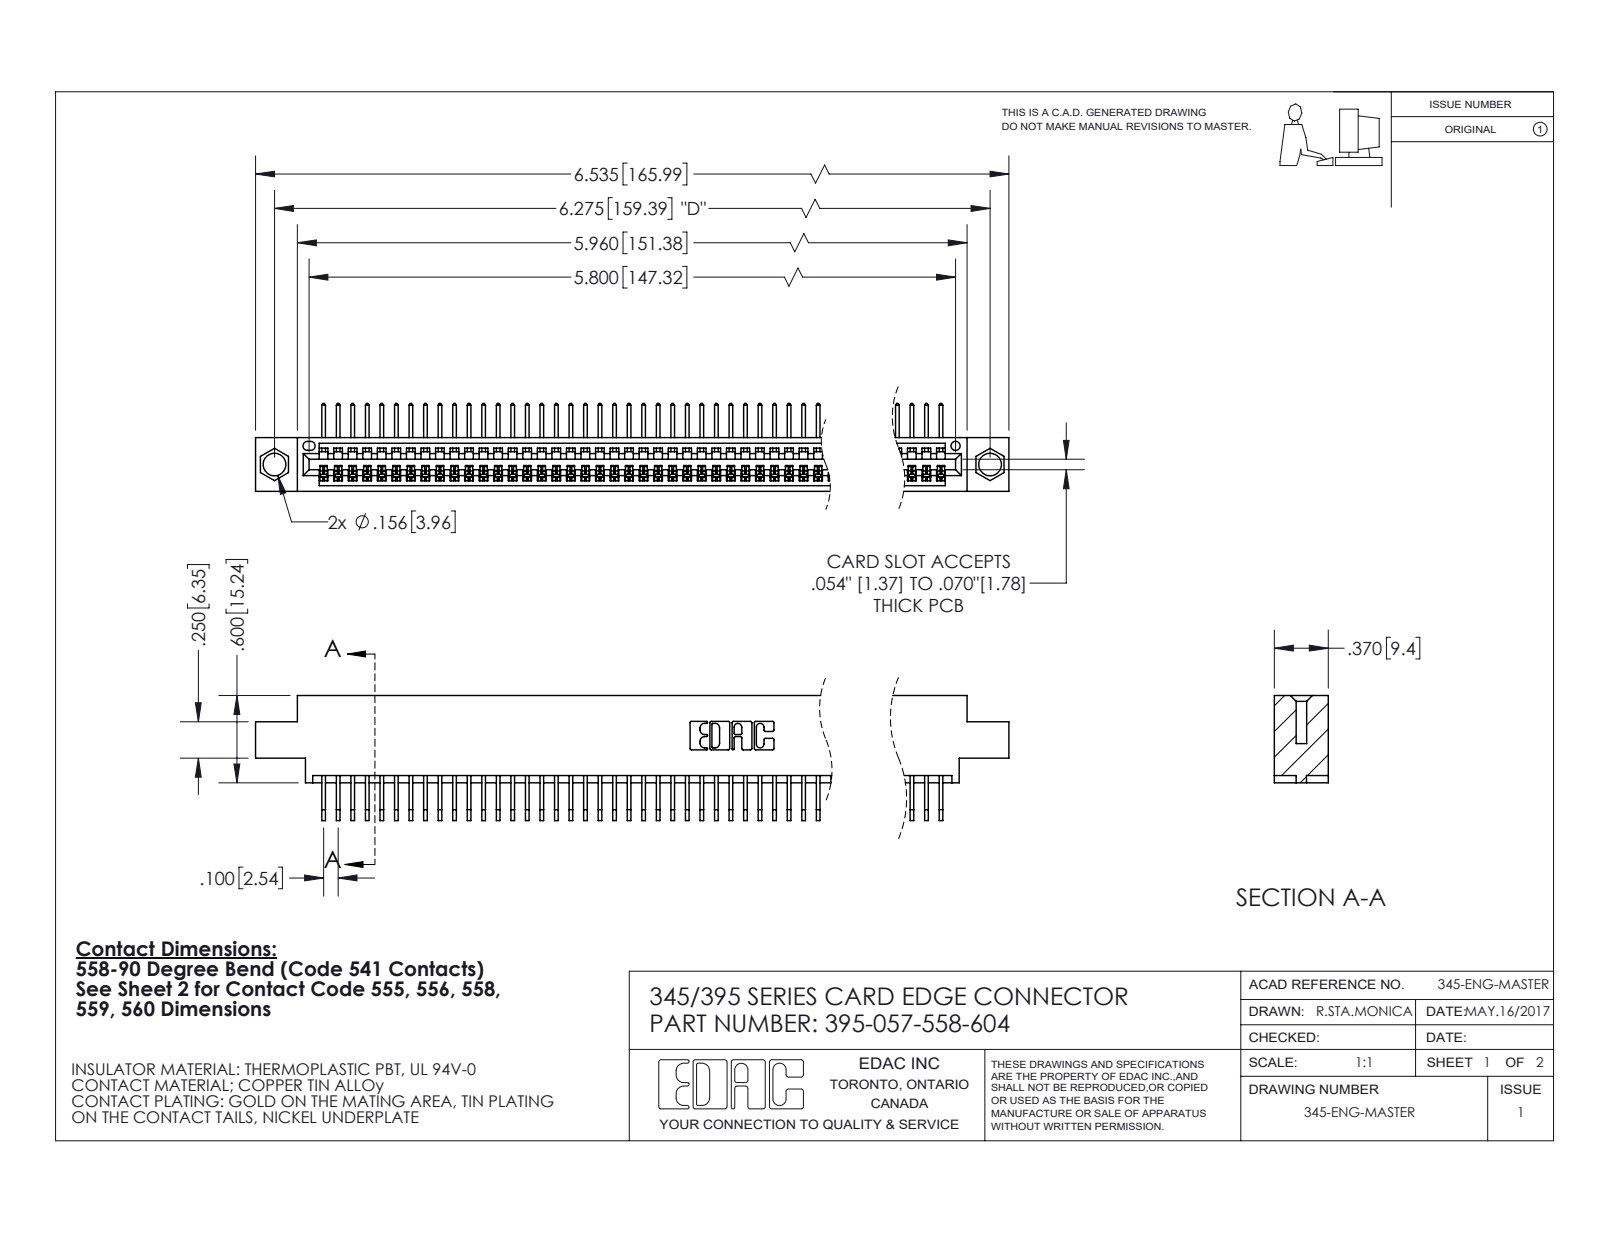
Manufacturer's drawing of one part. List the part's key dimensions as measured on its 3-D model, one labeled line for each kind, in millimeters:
Part name (STEP PRODUCT): 345 Part_0.170 Offset - 0.156 Dia-TI; 345-292-001_558 Tail - 2; 395-057-558-604
STEP written by: SolidWorks 2020 (CONFIG_CONTROL_DESIGN)
Units: millimetres
Bodies: 58 solids, 3564 faces (2492 planar, 1072 cylindrical, 0 other)
Overall size (bounding box): 166 × 21.8 × 15.4
Volume: 15 900 mm³ · Surface area: 22 360 mm²
Round holes (diameter × count): ⌀4 ×2, ⌀1.6 ×1
Partial cylindrical surfaces — rounded edges, fillets, slot ends (radius × count): R0.2 ×114, R0.3 ×22, R0.2 ×6, R0.8 ×6, R0.7 ×3, R0.8 ×2, R1 ×2, R0.4 ×1
Main face-to-face distances: 1.8, 7.6, 9.4, 5.1, 2.5, 6.9, 0.6, 5.7, 4.4, 3.8
Hole centre spacings: 6.9, 153.4, 159.4
